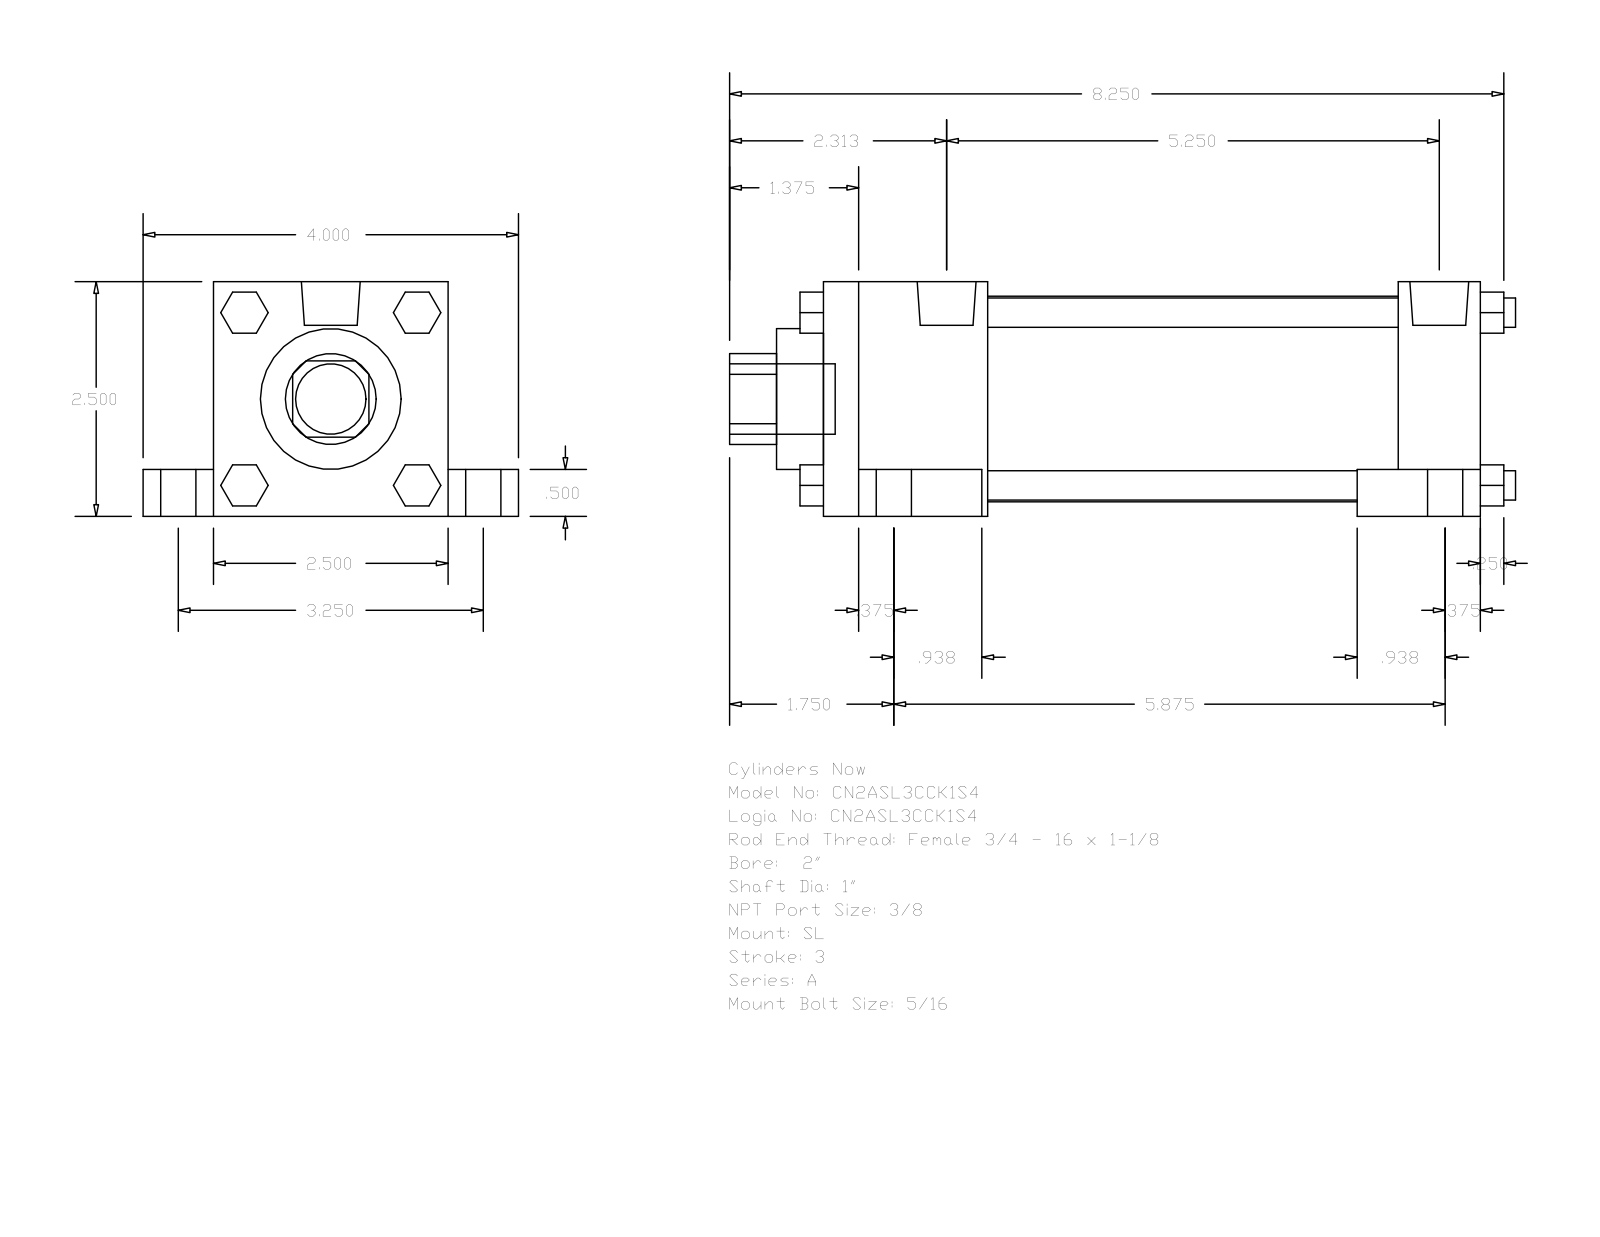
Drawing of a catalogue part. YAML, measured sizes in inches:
part_name: "A_SL__0200_1"
step_written_by: "GSSL Pune (CONFIG_CONTROL_DESIGN)"
units: inches
bodies: {solids: 0, faces: 148, planar: 112, cylindrical: 36, other: 0}
overall_size: [8.375, 4, 2.5]
round_holes:
  - {diameter: 1, count: 1}
  - {diameter: 1.5, count: 1}
  - {diameter: 2.19, count: 1}
round_bosses_or_shafts:
  - {diameter: 0.625, count: 4}
  - {diameter: 0.375, count: 4}
  - {diameter: 0.313, count: 4}
  - {diameter: 0.219, count: 4}
  - {diameter: 0.627, count: 2}
  - {diameter: 0.75, count: 1}
partial_cylinders:
  - {radius: 0.484, count: 1}
face_to_face_distances: [2.5, 7, 0.5, 2, 0.75, 3.25, 0.375, 1.75, 5.25, 6.125]
